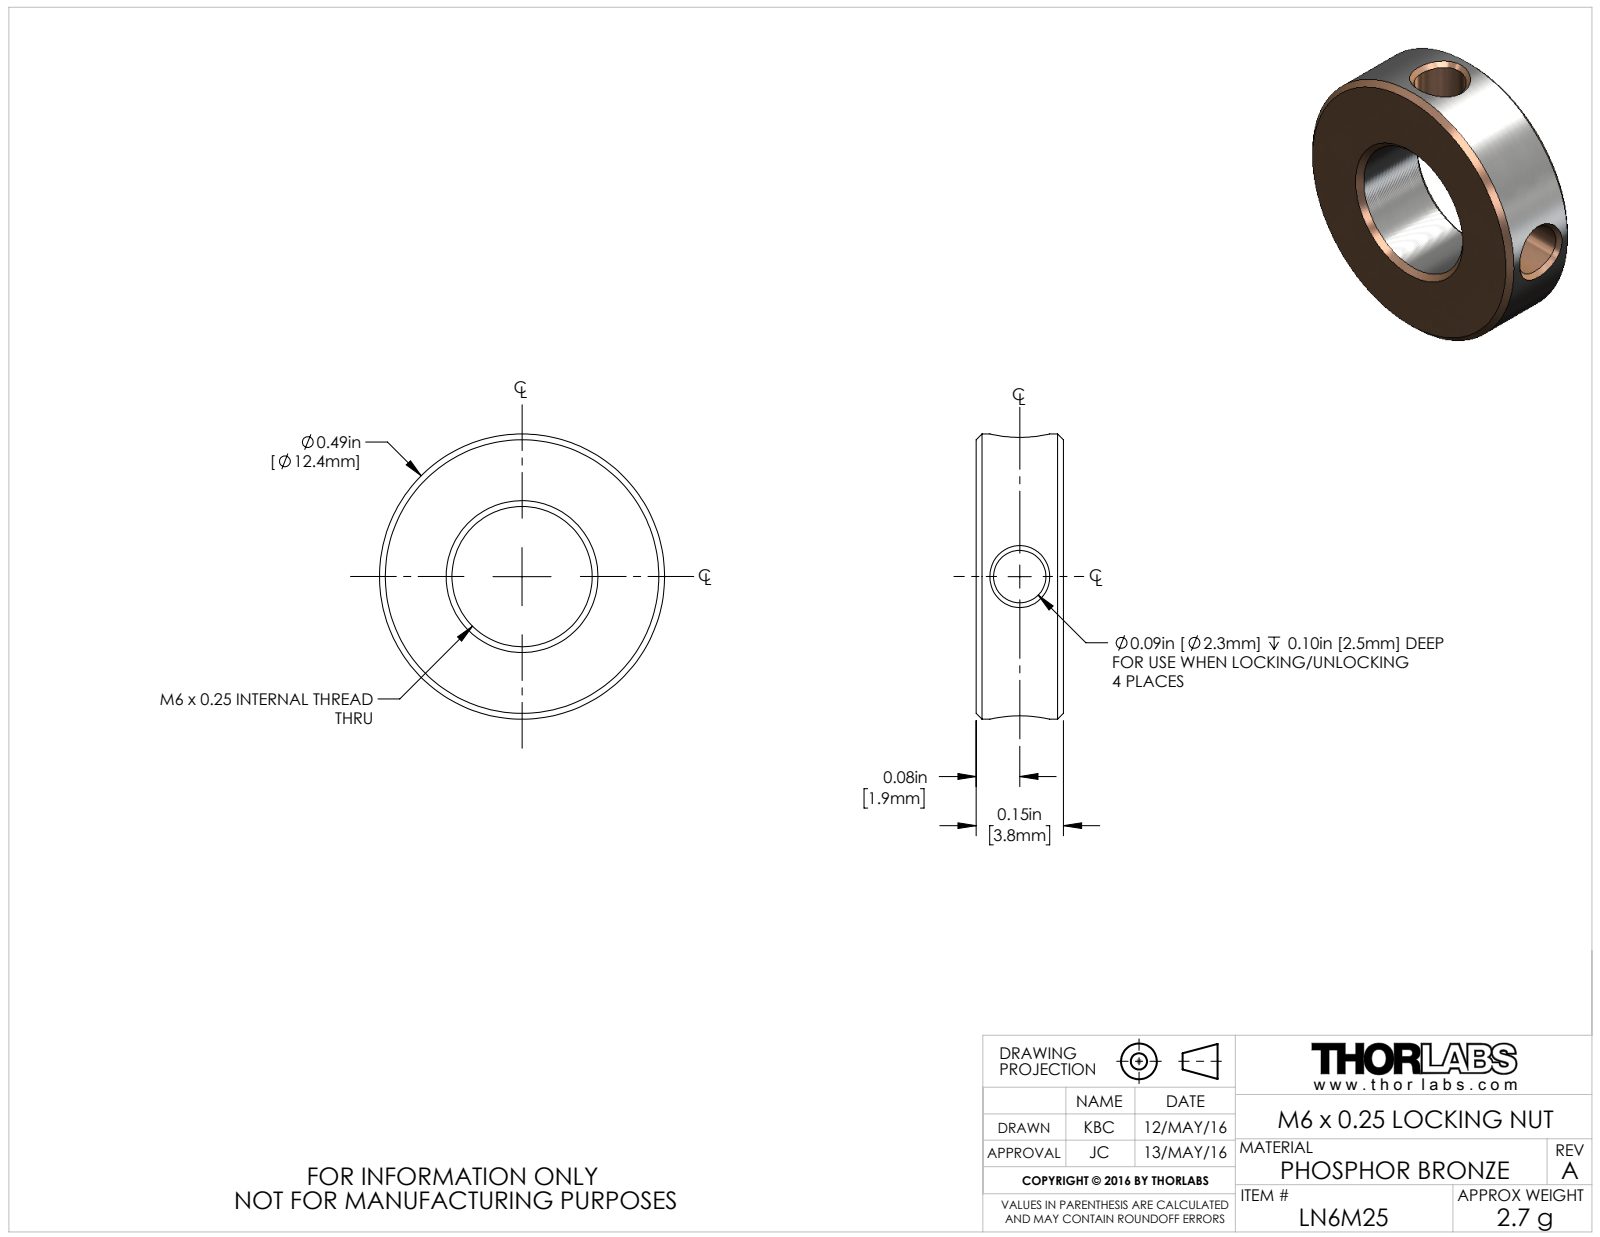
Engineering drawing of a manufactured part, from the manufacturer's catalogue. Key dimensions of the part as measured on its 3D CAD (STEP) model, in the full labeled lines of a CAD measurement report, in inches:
Part name (STEP PRODUCT): TTN102544-E0W
STEP written by: SolidWorks 2016 (CONFIG_CONTROL_DESIGN)
Units: inches
Bodies: 1 solid, 34 faces (6 planar, 12 cylindrical, 16 other)
Overall size (bounding box): 0.49 × 0.49 × 0.15
Volume: 0.019 in³ · Surface area: 0.708 in²
Round holes (diameter × count): ⌀0.09 ×2, ⌀0.241 ×1
Round bosses / shafts (diameter × count): ⌀0.49 ×1
Main face-to-face distances: 0.15, 0.29
